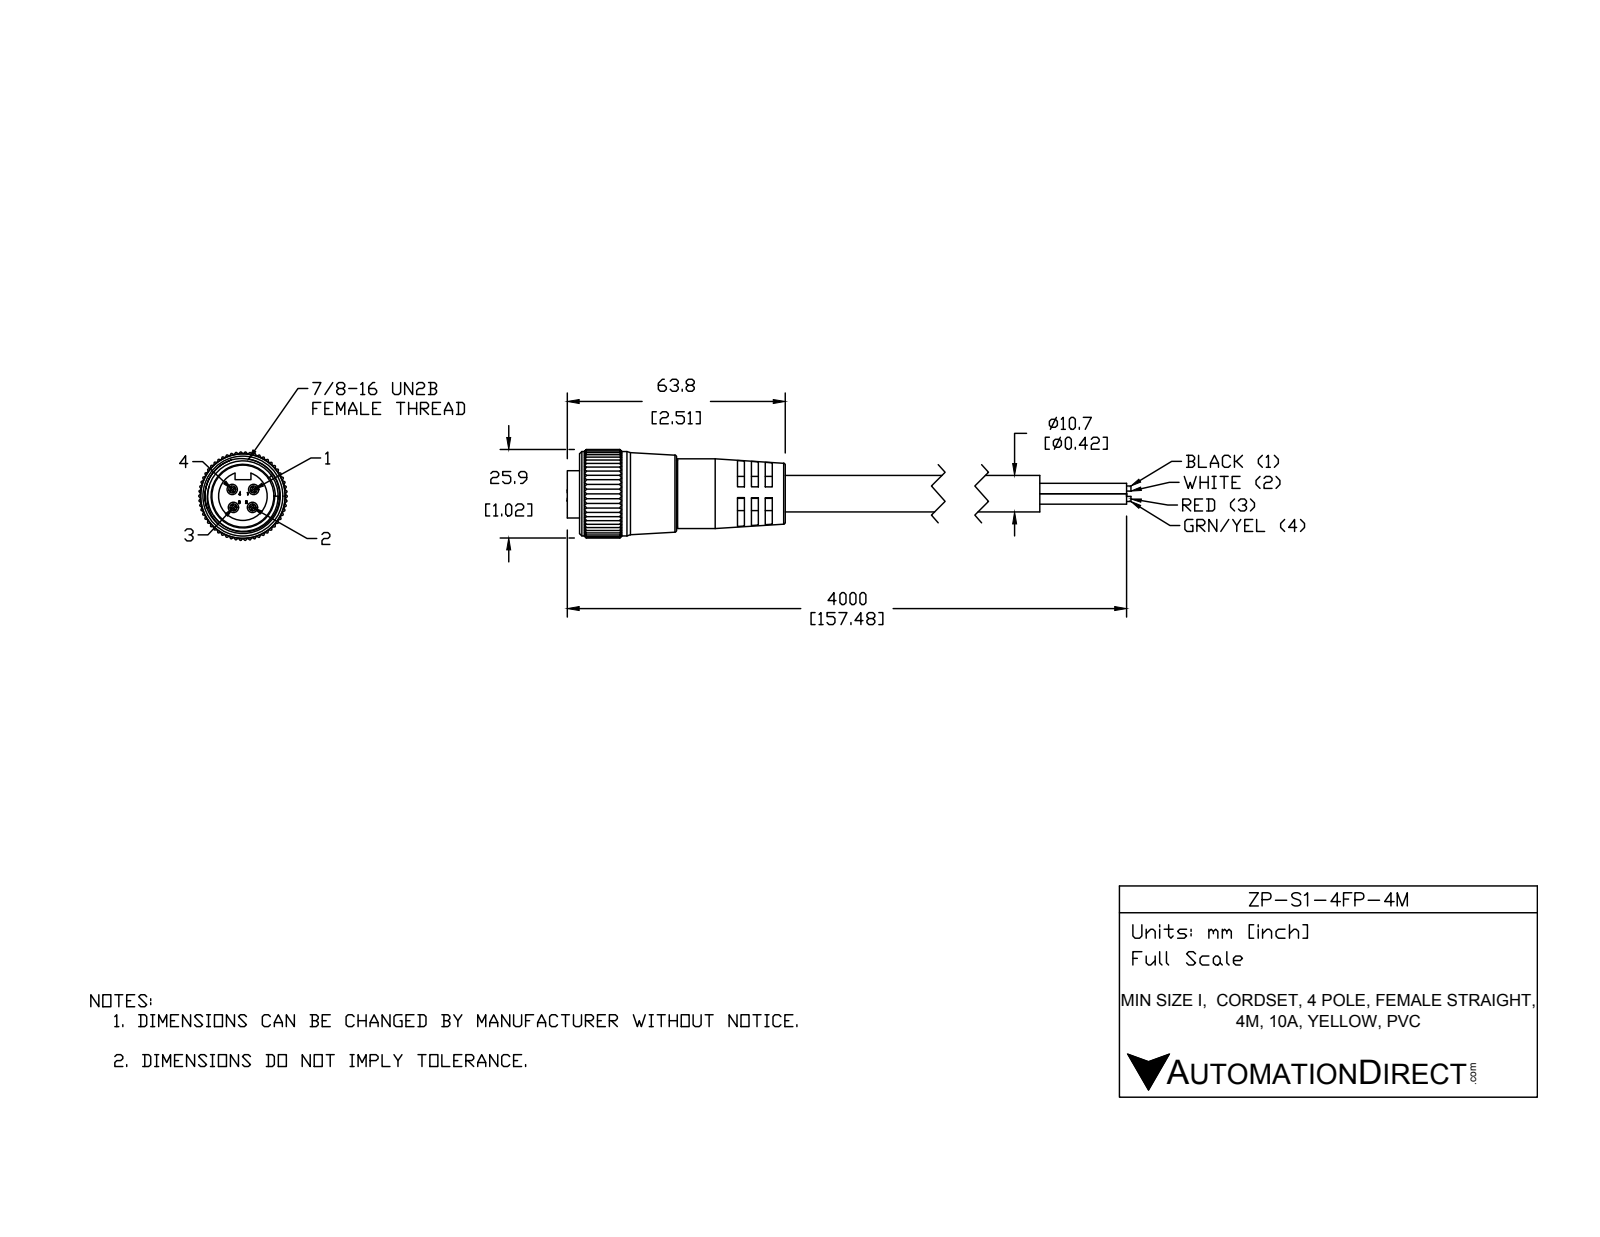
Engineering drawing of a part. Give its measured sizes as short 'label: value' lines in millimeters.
name: ZP-S1-4FP-4M
written by: SolidWorks 2015 (AUTOMOTIVE_DESIGN)
unit: mm
bodies: 2 solids, 558 faces (208 planar, 308 cylindrical, 42 other)
size: 109.09 × 52.91 × 25.84
volume: 27 613 mm³; area: 12 011 mm²
holes: 4× ⌀3.05, 1× ⌀18.14, 1× ⌀20.58, 1× ⌀21
bosses: 2× ⌀10.67, 1× ⌀24.68, 1× ⌀20.4, 1× ⌀19.5, 1× ⌀14.22
rounds: 165× R0.25, 1× R5.25, 1× R12.93
face distances: 4.03, 2, 2.03, 6.03, 8.06, 13.87, 11.87, 9.84, 7.84, 6.06
hole spacings: 3.67, 5.24, 4.32, 4.33, 5.59, 6.24, 7.89, 7.9
